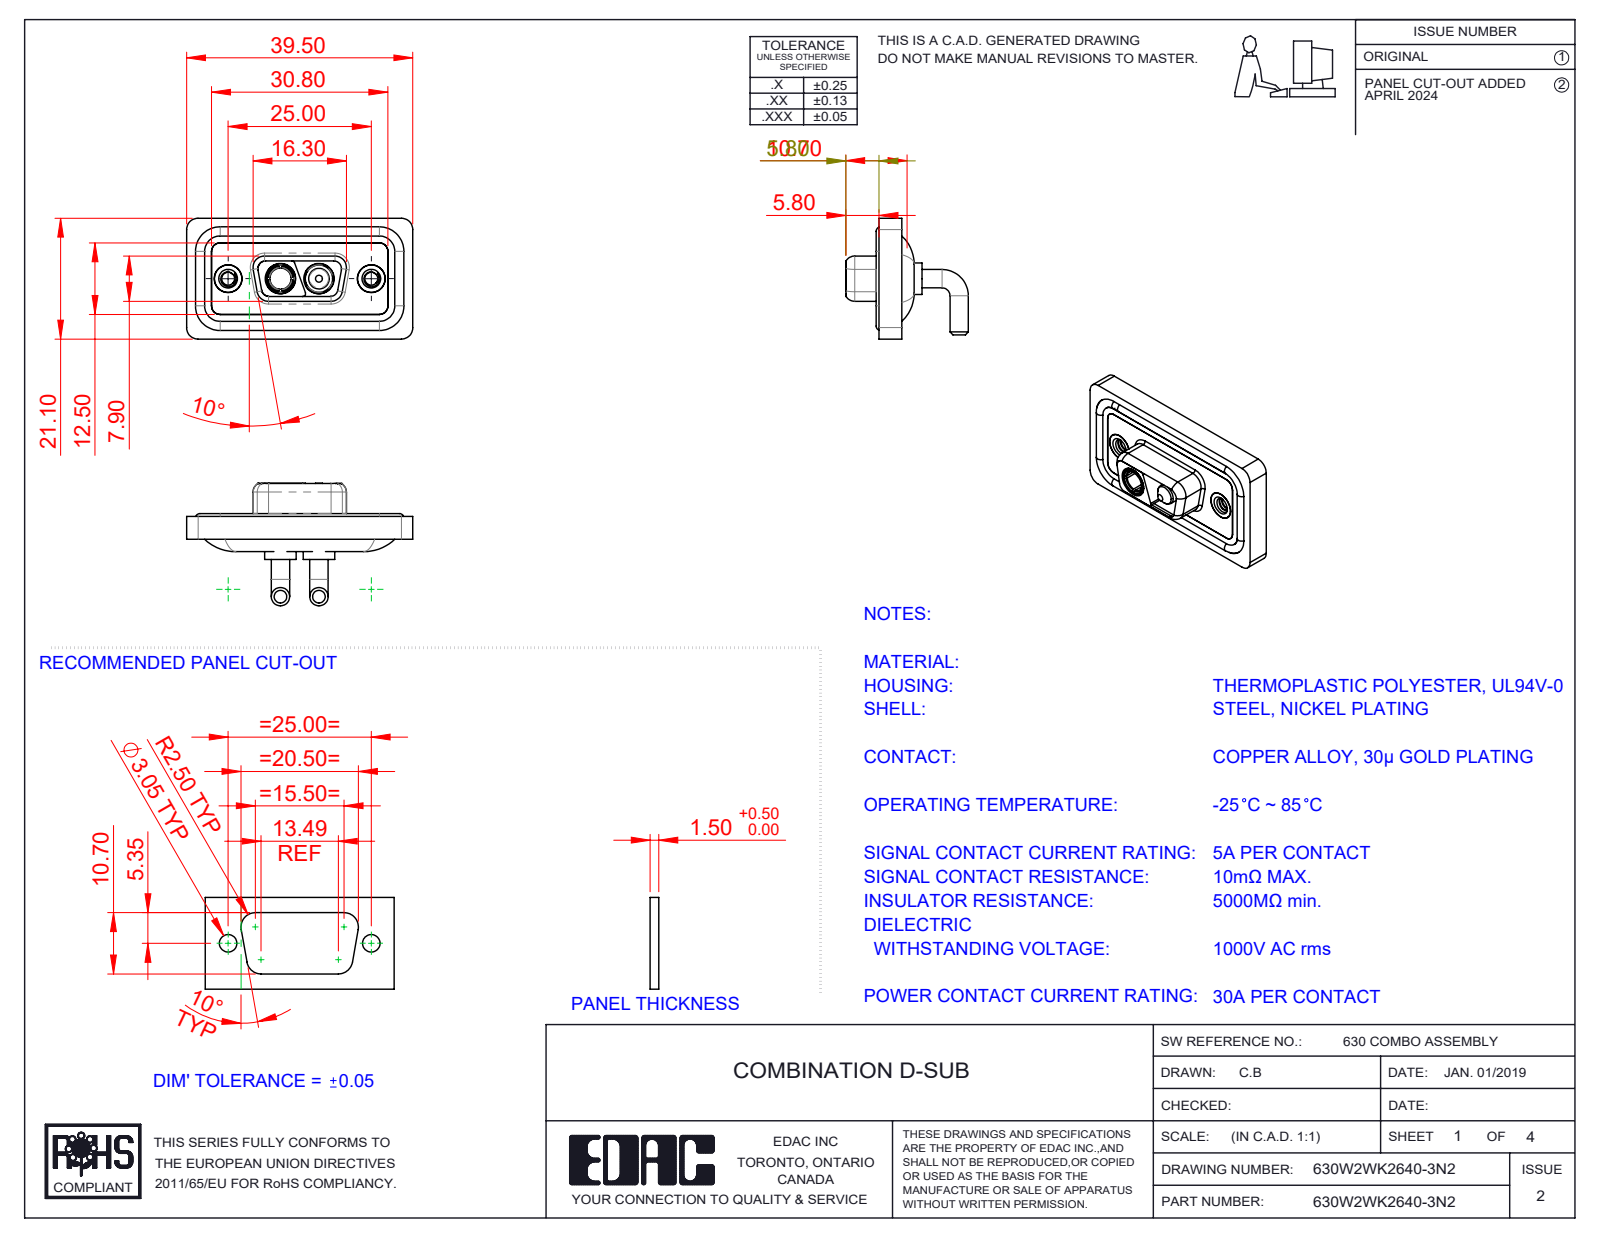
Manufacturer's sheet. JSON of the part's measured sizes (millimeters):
{"part_name": "630Combo Shell Rear_09 Contacts; 630Combo Waterproof Housing_09 Contacts; 630Combo Threaded Rivet_2; 630Combo Housing_2WK2 (+4 more)", "step_written_by": "SolidWorks 2023 (CONFIG_CONTROL_DESIGN)", "units": "millimeters", "bodies": {"solids": 11, "faces": 508, "planar": 144, "cylindrical": 235, "other": 129}, "overall_size": [39.5, 21.4, 21.1], "volume_mm3": 4763, "surface_area_mm2": 7531, "round_holes": [[4.85, 4], [2.26, 2], [4, 2], [4.05, 2], [5, 2], [5.3, 2], [3.7, 1]], "round_bosses_or_shafts": [[3.2, 4], [1.6, 4], [5.5, 2], [5.2, 2], [4.95, 2], [4.8, 2], [4.75, 2], [3.75, 2]], "partial_cylinders_radius": [[1.5, 18], [2, 18], [1.35, 8], [1.6, 8], [0.5, 6], [0.25, 4], [0.6, 4], [0.65, 4]], "face_to_face_distances": [0.4, 1.1, 2.9, 1.8, 2.5, 1.6, 3.1, 1.5, 2.1, 3.7], "hole_center_spacings": [9.14, 15.86, 6.72, 25]}
